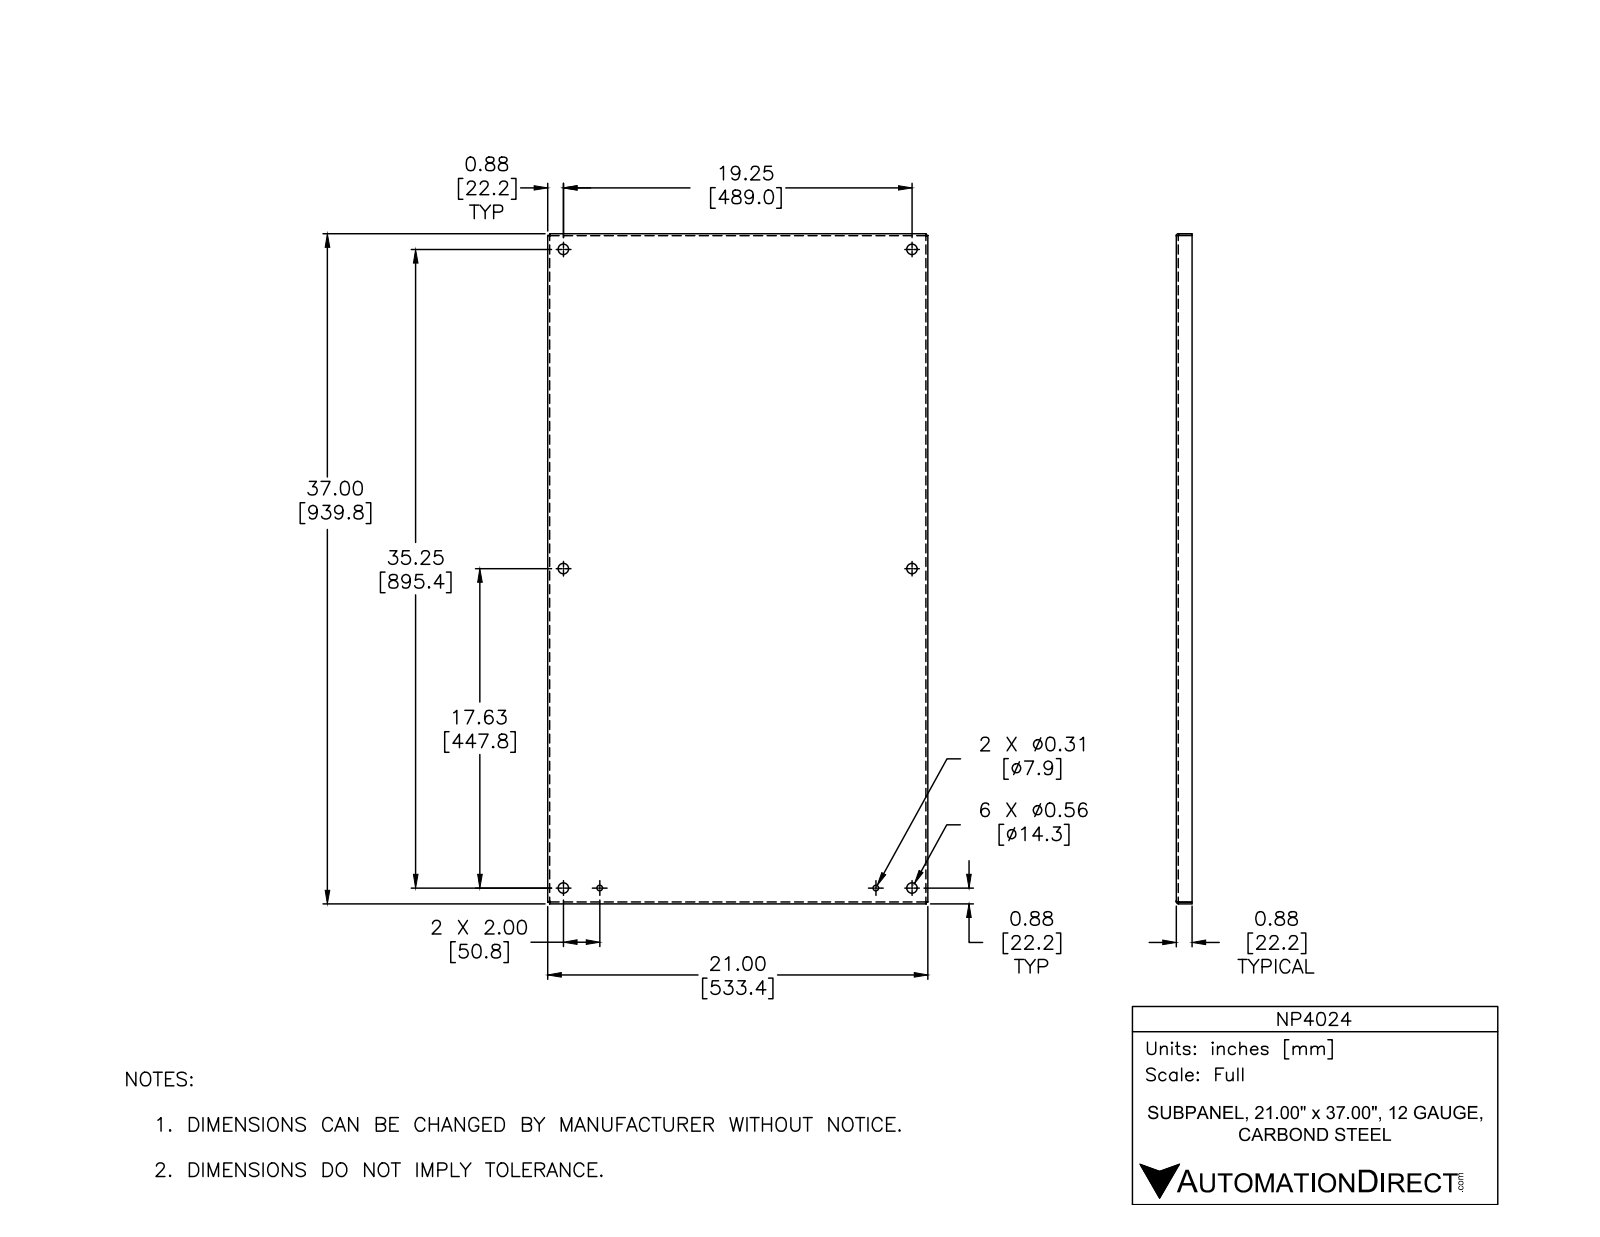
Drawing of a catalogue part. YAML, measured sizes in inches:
part_name: "NP4024"
step_written_by: "Autodesk Inventor 2012 (AUTOMOTIVE_DESIGN)"
units: inches
bodies: {solids: 1, faces: 46, planar: 22, cylindrical: 16, other: 8}
overall_size: [37, 21, 0.875]
volume: 80.76
surface_area: 1735
round_holes:
  - {diameter: 0.563, count: 6}
  - {diameter: 0.312, count: 2}
partial_cylinders:
  - {radius: 0.031, count: 4}
  - {radius: 0.125, count: 4}
face_to_face_distances: [0.094, 20.906, 36.906, 21, 20.813, 36.813, 37, 0.781, 0.875, 0.105]
hole_center_spacings: [17.625, 26.1, 19.25, 17.738, 35.25, 35.307, 39.245, 40.164]
